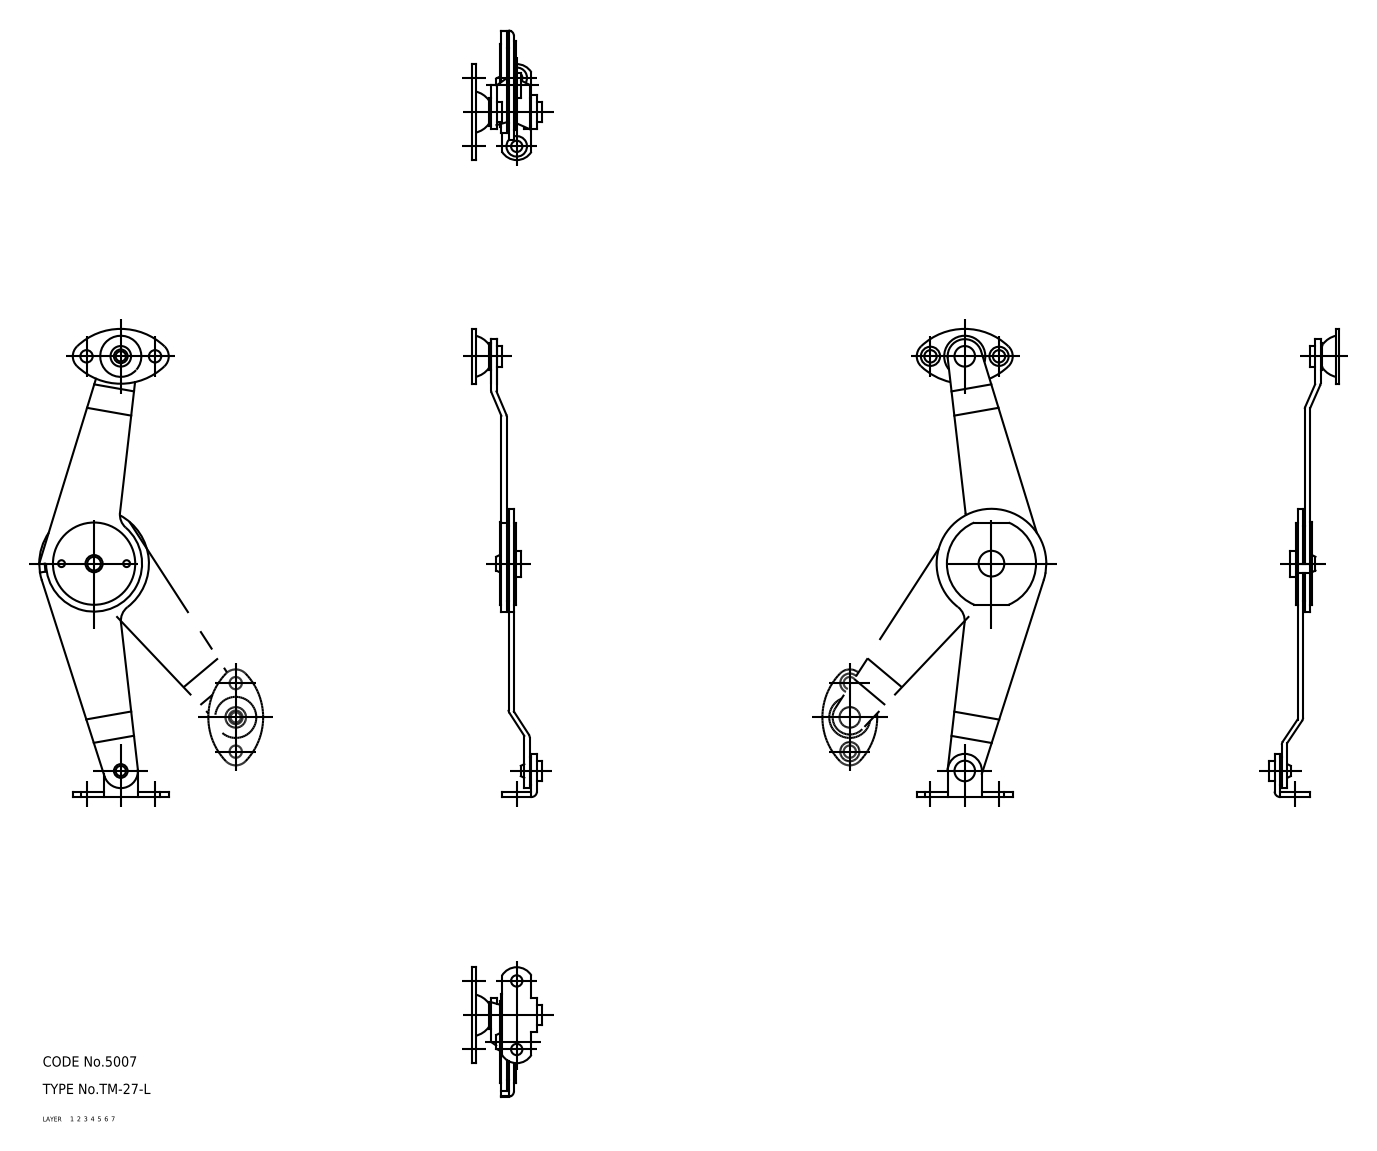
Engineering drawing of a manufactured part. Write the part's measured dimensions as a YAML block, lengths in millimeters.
part_name: "rivet_A1; rivet_A2; washer_2; ball (+8 more)"
step_written_by: "CADfix (AUTOMOTIVE_DESIGN)"
units: millimeters
bodies: {solids: 13, faces: 155, planar: 0, cylindrical: 0, other: 155}
overall_size: [136.6, 37.8, 20.4]
volume: 6515
surface_area: 10644
